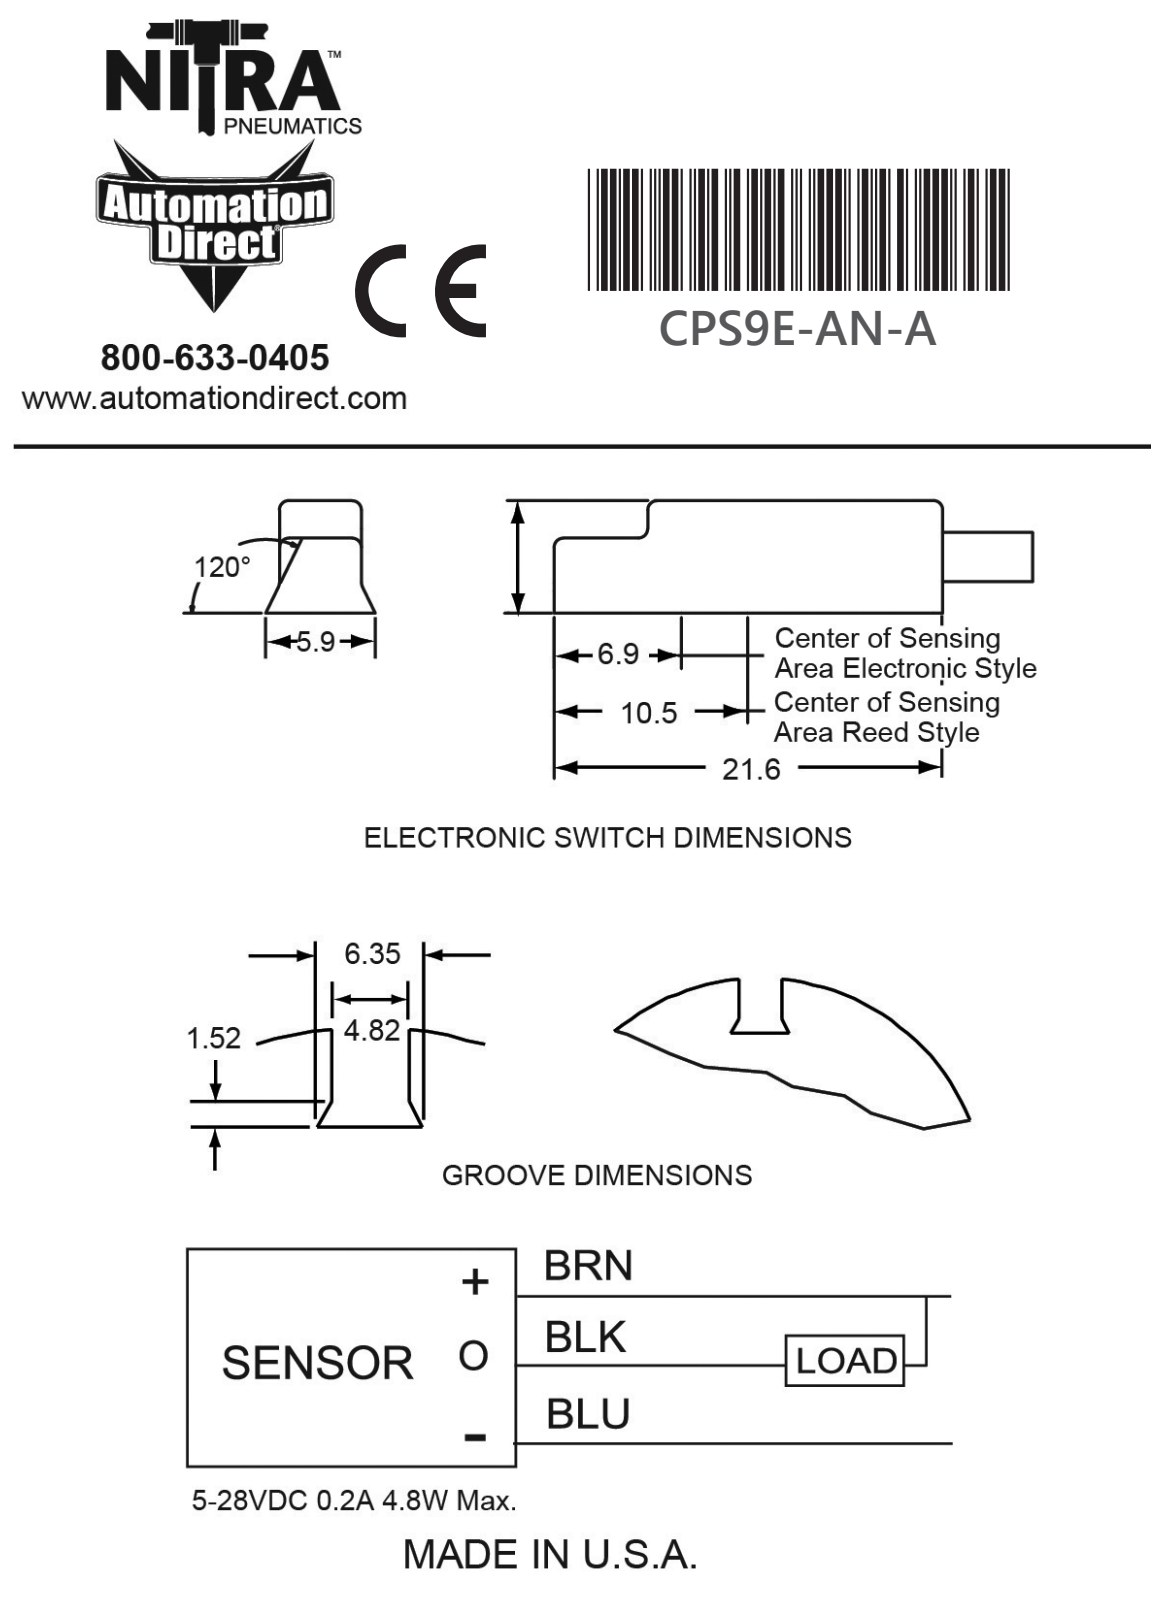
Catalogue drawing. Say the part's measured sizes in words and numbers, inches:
The part is named "CPS9E-AN-A". Its 3-D file was written by "SolidWorks 2023 (CONFIG_CONTROL_DESIGN)". It is 1 solid with 83 faces: 24 planar, 41 cylindrical and 18 other. Overall it measures 6.21 by 0.24 by 0.234 inches. Its volume is 0.07 cubic inches and its surface area 2.487 square inches. Round holes: 1 of diameter 0.094, 1 of diameter 0.125. Round bosses or shafts: 3 of diameter 0.031, 3 of diameter 0.016, 1 of diameter 0.105. Partial cylindrical surfaces (rounded edges, fillets, slot ends): 20 of radius 0.02. The main face-to-face distances are 0.175, 0.241, 0.85, 0.161, 0.08, 0.156, 0.235, 3.86, 4.71, 4.51. The hole center spacings are 0.172.
